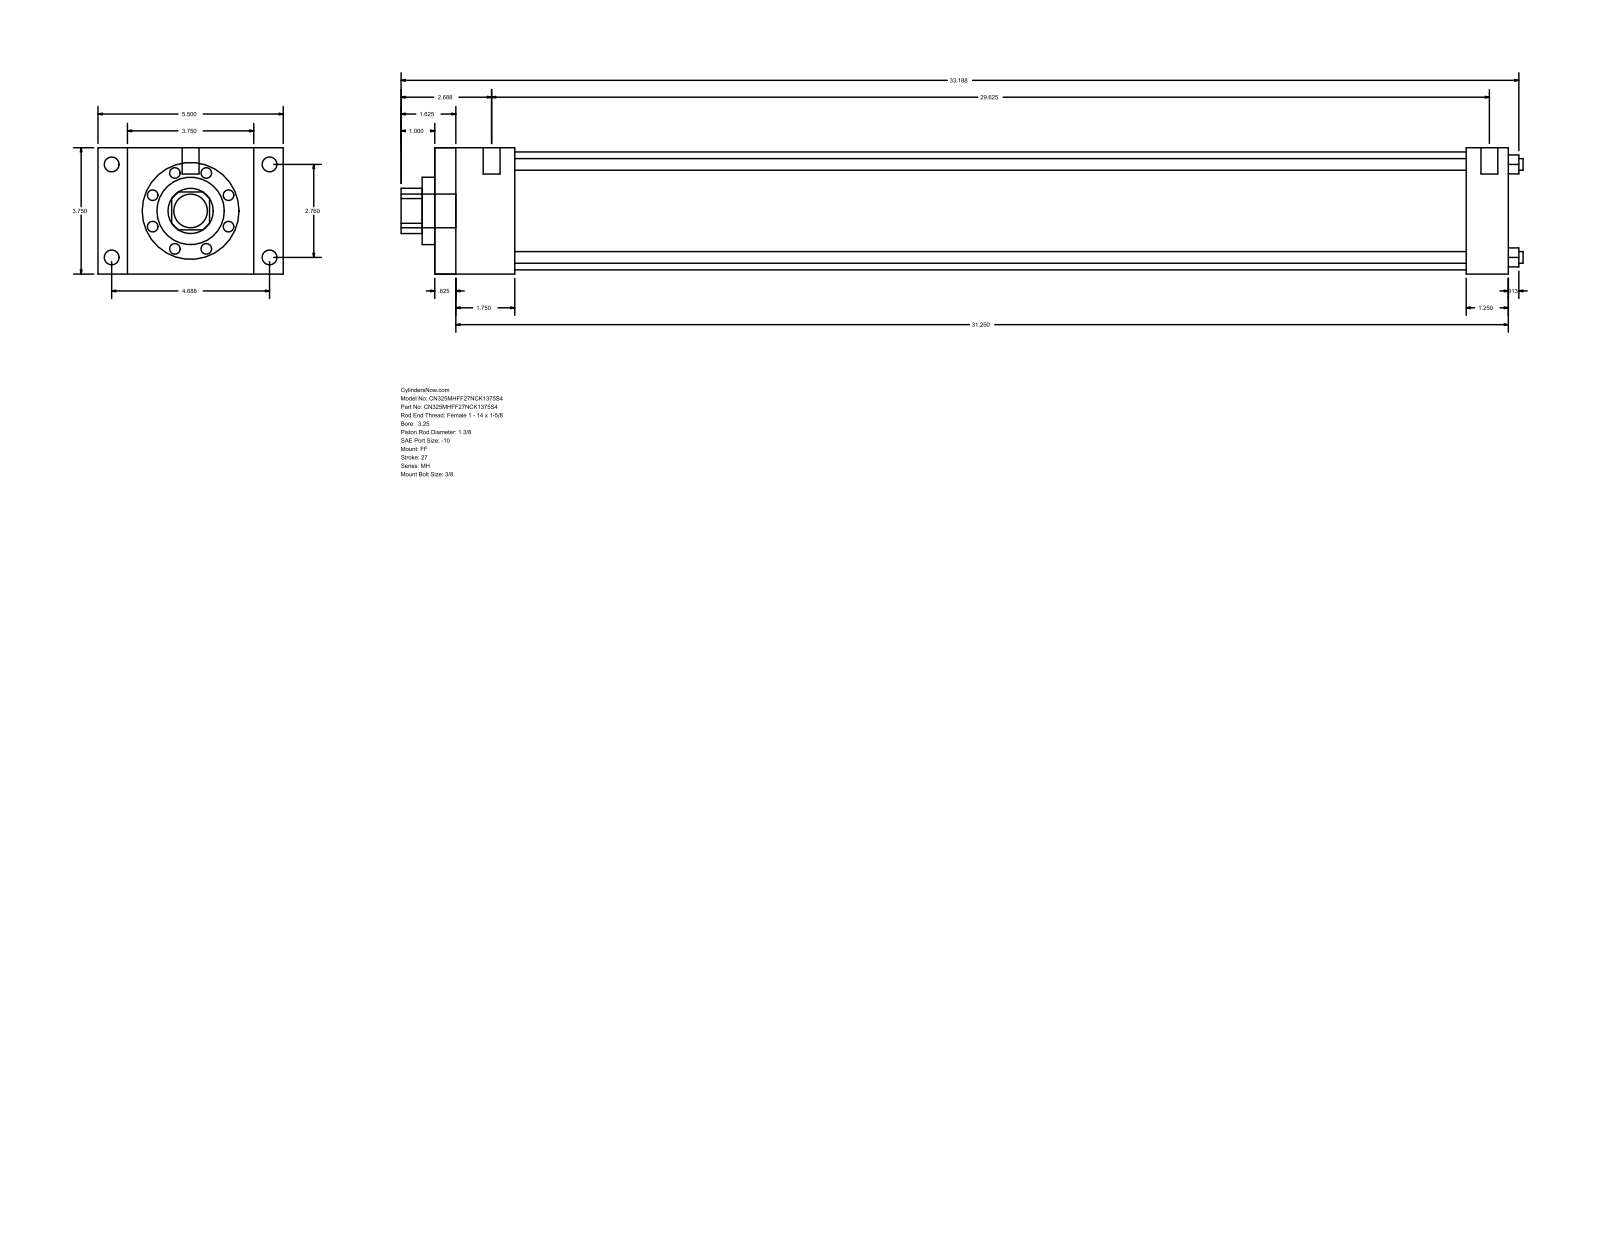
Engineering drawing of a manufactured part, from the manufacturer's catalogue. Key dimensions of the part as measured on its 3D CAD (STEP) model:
Part name (STEP PRODUCT): MH_FF__0325_1.375
STEP written by: GSSL Pune (CONFIG_CONTROL_DESIGN)
Units: millimetres
Bodies: 0 solids, 92 faces (64 planar, 28 cylindrical, 0 other)
Overall size (bounding box): 846.14 × 139.7 × 95.25
Round holes (diameter × count): ⌀8.76 ×4, ⌀34.92 ×1, ⌀50.8 ×1, ⌀88.9 ×1
Round bosses / shafts (diameter × count): ⌀11.13 ×4, ⌀5.56 ×4, ⌀12.7 ×2, ⌀25.4 ×1
Partial cylindrical surfaces — rounded edges, fillets, slot ends (radius × count): R17.06 ×1
Main face-to-face distances: 95.24, 809.62, 15.87, 793.75, 22.23, 117.47, 777.87, 762, 31.75, 60.32
Hole centre spacings: 49.57, 70.1, 99.14
